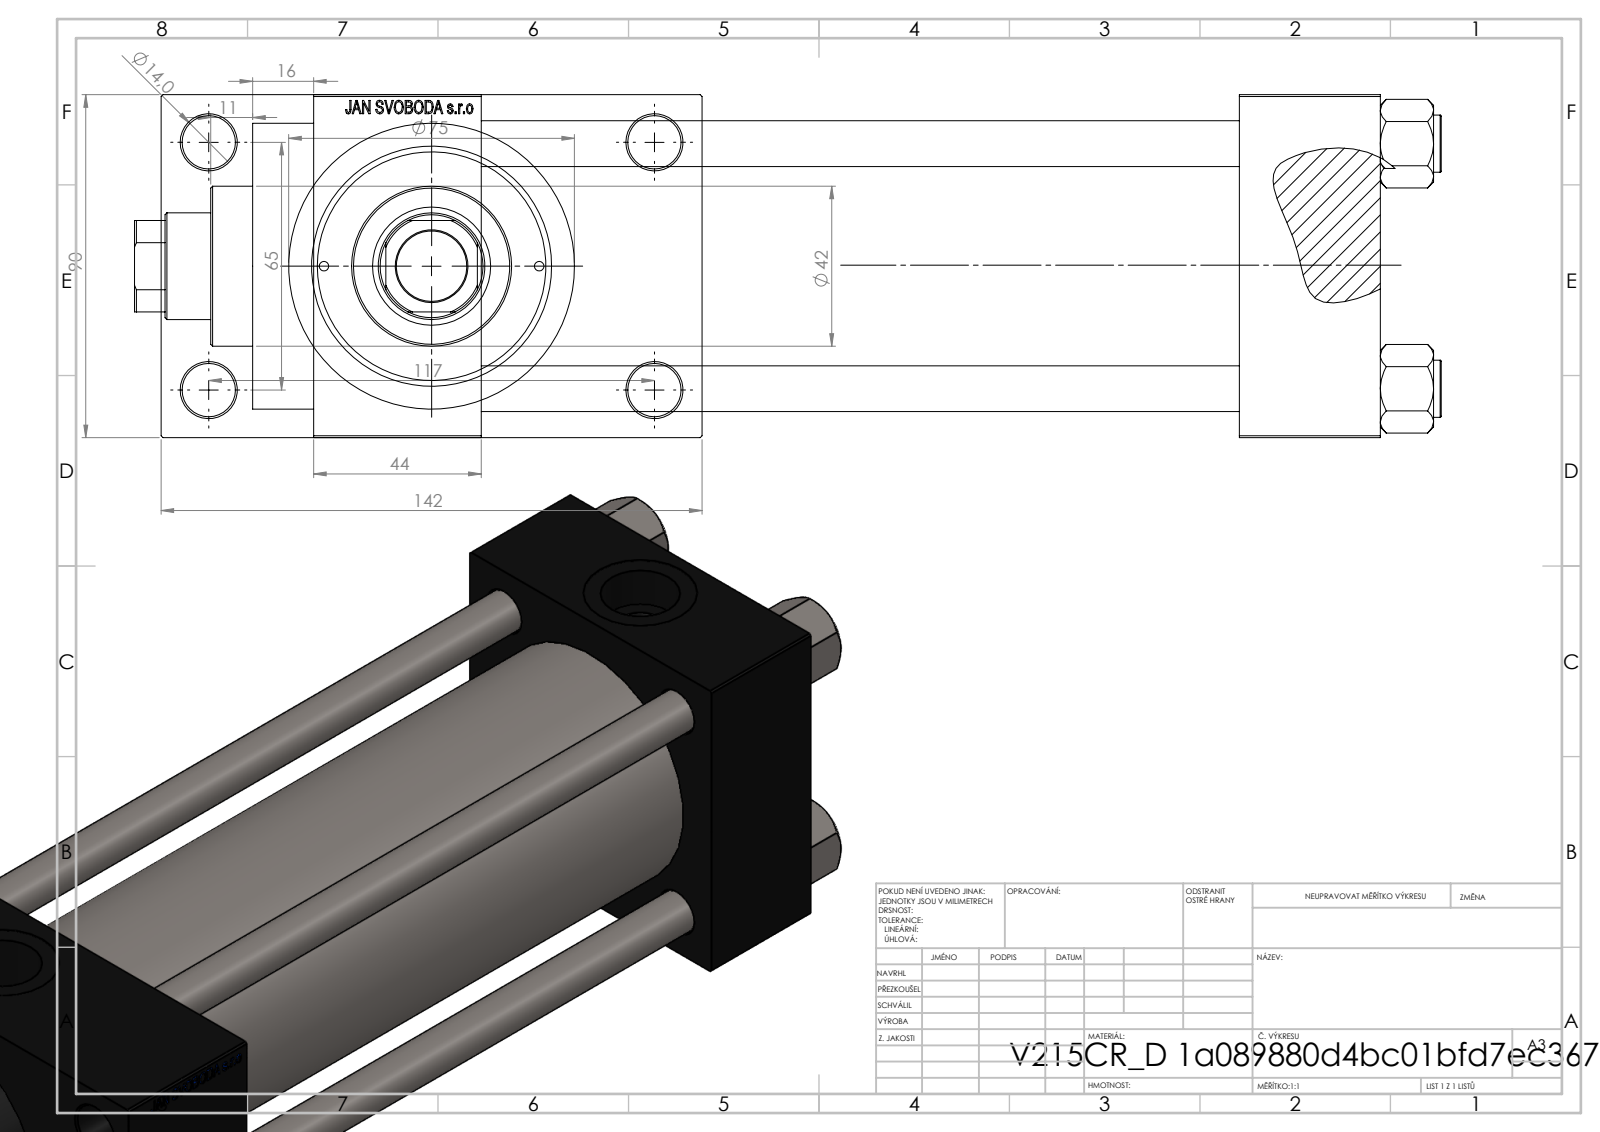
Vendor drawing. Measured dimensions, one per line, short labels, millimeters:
name: V215CR_D_TYCINKA; NUT_M5_D; V215CR_D_Body; V215_VC_A (+1 more)
written by: SolidWorks 2019 (CONFIG_CONTROL_DESIGN)
unit: mm
bodies: 11 solids, 1112 faces (499 planar, 93 cylindrical, 520 other)
size: 343 × 142 × 90
volume: 1 342 000 mm³; area: 290 006 mm²
holes: 4× ⌀12, 4× ⌀14, 2× ⌀2.5, 2× ⌀7, 2× ⌀20.96, 2× ⌀30, 1× ⌀18.5, 1× ⌀28, 1× ⌀31, 1× ⌀50, 1× ⌀60, 1× ⌀63
bosses: 4× ⌀15, 1× ⌀75, 1× ⌀69, 1× ⌀42
rounds: 1× R13.5
face distances: 90, 199, 37, 236, 243, 280, 44, 26, 116, 142
hole spacings: 26.35, 32.39, 44.4, 45.47, 64.3, 66.92, 68.42, 69.81
